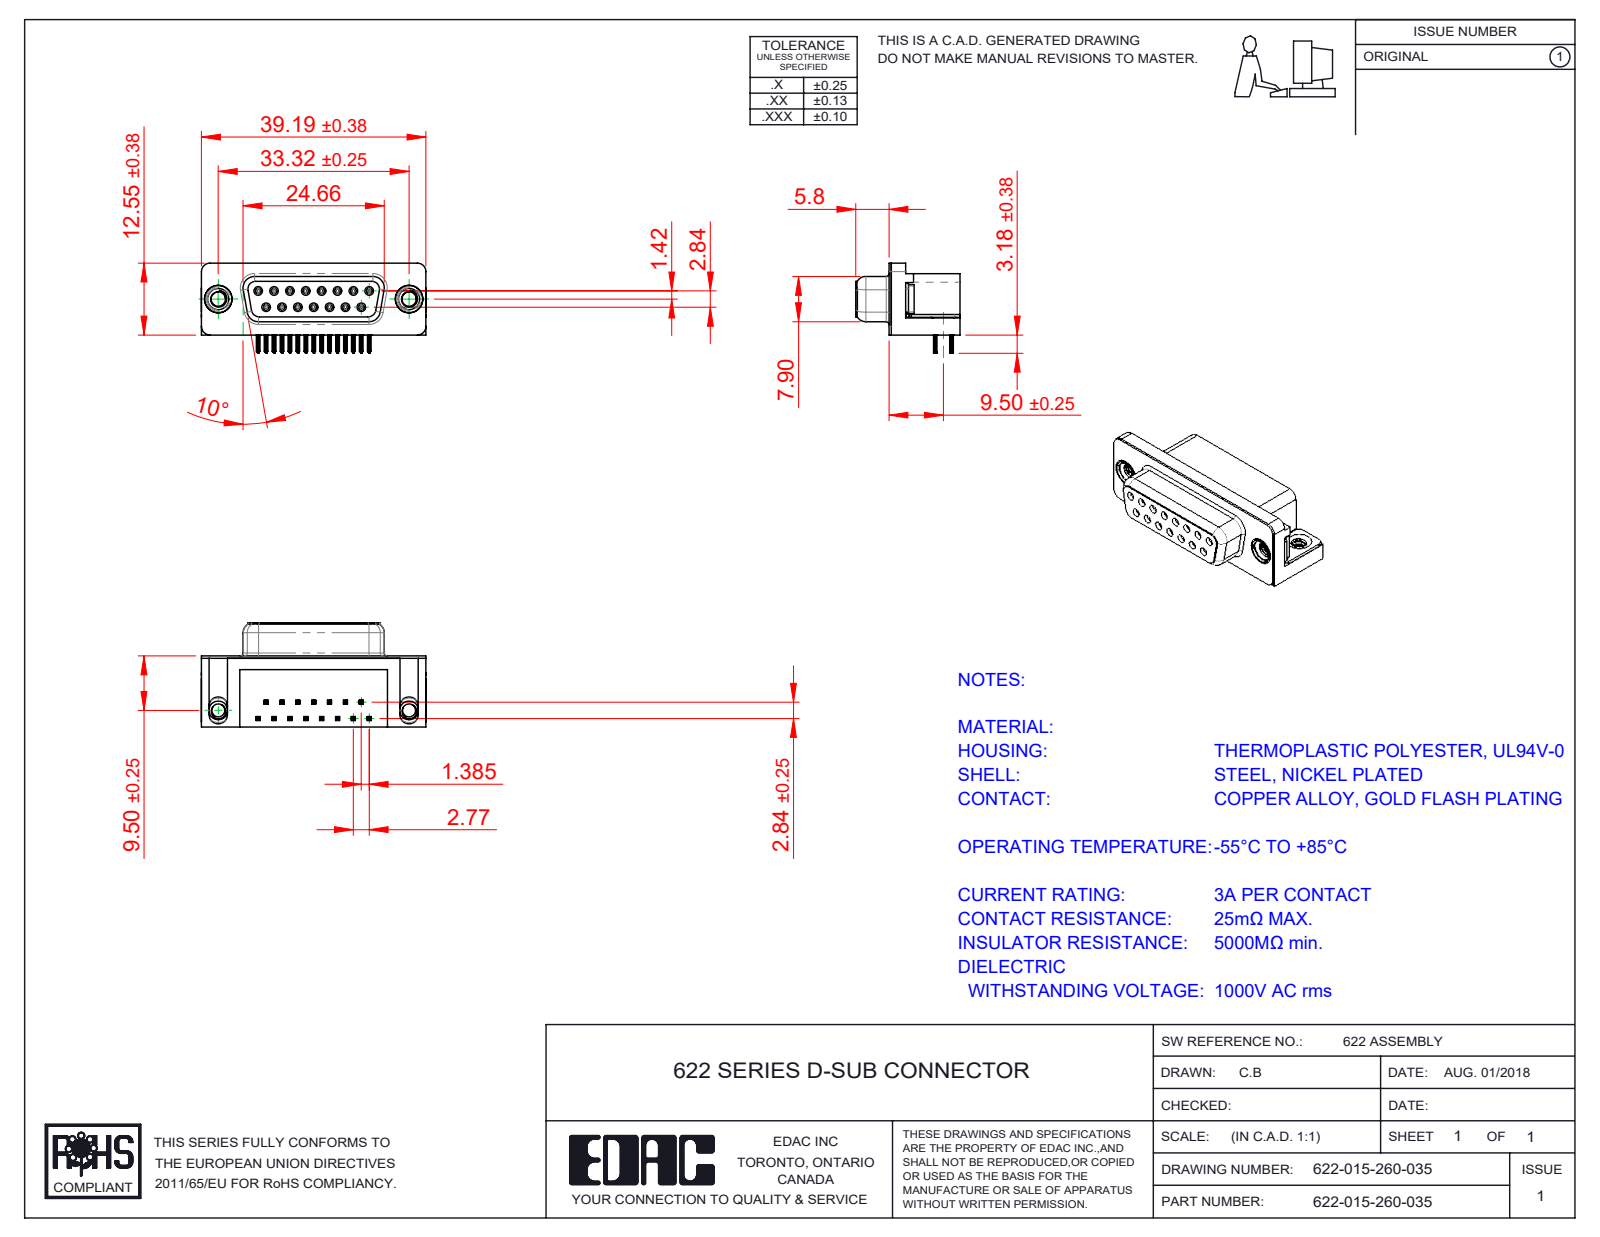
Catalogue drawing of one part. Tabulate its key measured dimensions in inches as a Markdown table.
| quantity | value |
| --- | --- |
| part name | 622 Socket Bottom; 622 Contact Top; 622 Housing_15 Socket; 622 Shell_15 Socket (+3 more) |
| STEP written by | SolidWorks 2016 (CONFIG_CONTROL_DESIGN) |
| units | inches |
| bodies | 21 solids, 2467 faces (1106 planar, 617 cylindrical, 744 other) |
| overall size | 1.544 × 0.717 × 0.64 |
| volume | 0.316 in³ |
| surface area | 10.42 in² |
| round holes (diameter × count) | 0.031 × 15, 0.035 × 15, 0.098 × 2, 0.157 × 2, 0.189 × 2, 0.197 × 2 |
| round bosses / shafts (diameter × count) | 0.047 × 15, 0.193 × 2, 0.187 × 2, 0.154 × 2 |
| partial cylindrical surfaces (radius × count) | 0.004 × 120, 0.006 × 60, 0.014 × 30, 0.039 × 18, 0.013 × 15, 0.02 × 10, 0.01 × 8, 0.053 × 8 |
| main face-to-face distances | 0.016, 0.472, 0.244, 0.488, 0.407, 0.114, 0.033, 0.262, 0.014, 0.02 |
| hole center spacings | 0.124, 0.109, 0.218, 0.327, 0.436, 0.198, 0.198, 0.294 |
